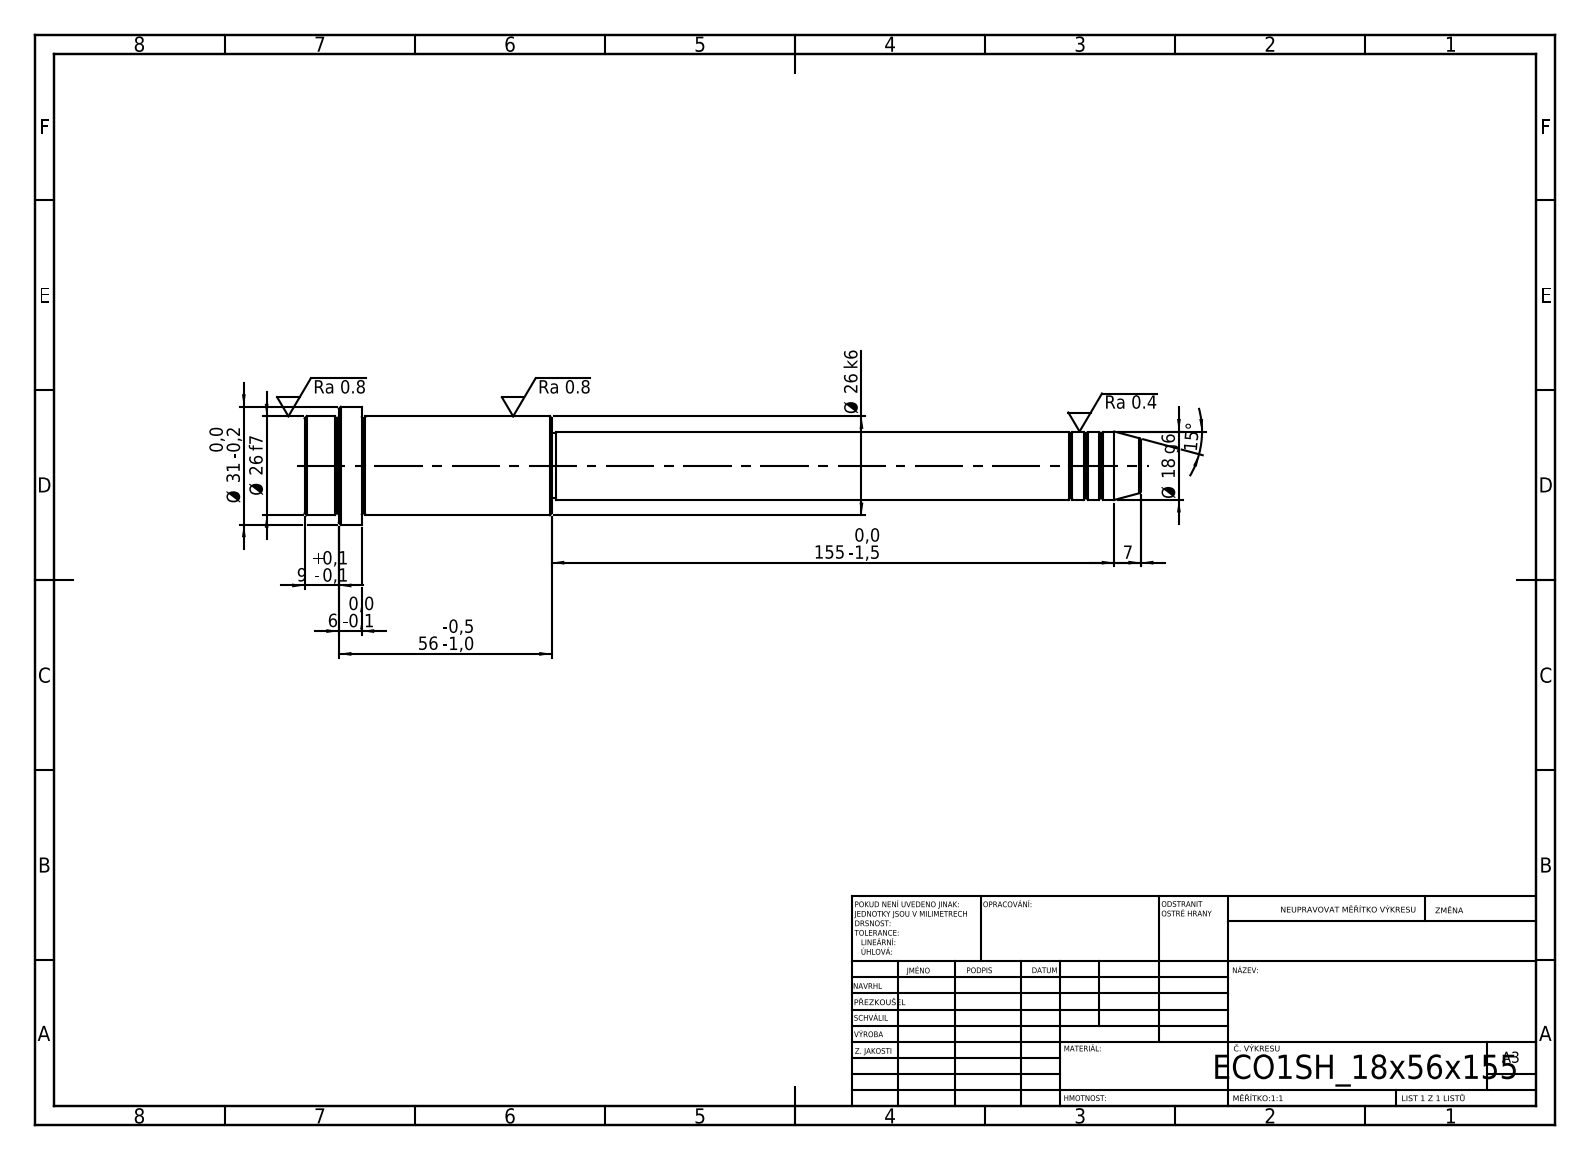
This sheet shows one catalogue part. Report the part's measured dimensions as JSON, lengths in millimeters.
{"step_written_by": "SolidWorks 2019 (CONFIG_CONTROL_DESIGN)", "units": "millimeters", "bodies": {"solids": 1, "faces": 52, "planar": 6, "cylindrical": 16, "other": 30}, "overall_size": [220, 31, 31], "volume_mm3": 74762, "surface_area_mm2": 15698, "round_bosses_or_shafts": [[31, 1], [26, 1], [18, 1], [17, 1]], "face_to_face_distances": [65, 50, 15, 56, 6, 9, 155, 205, 211, 220]}
